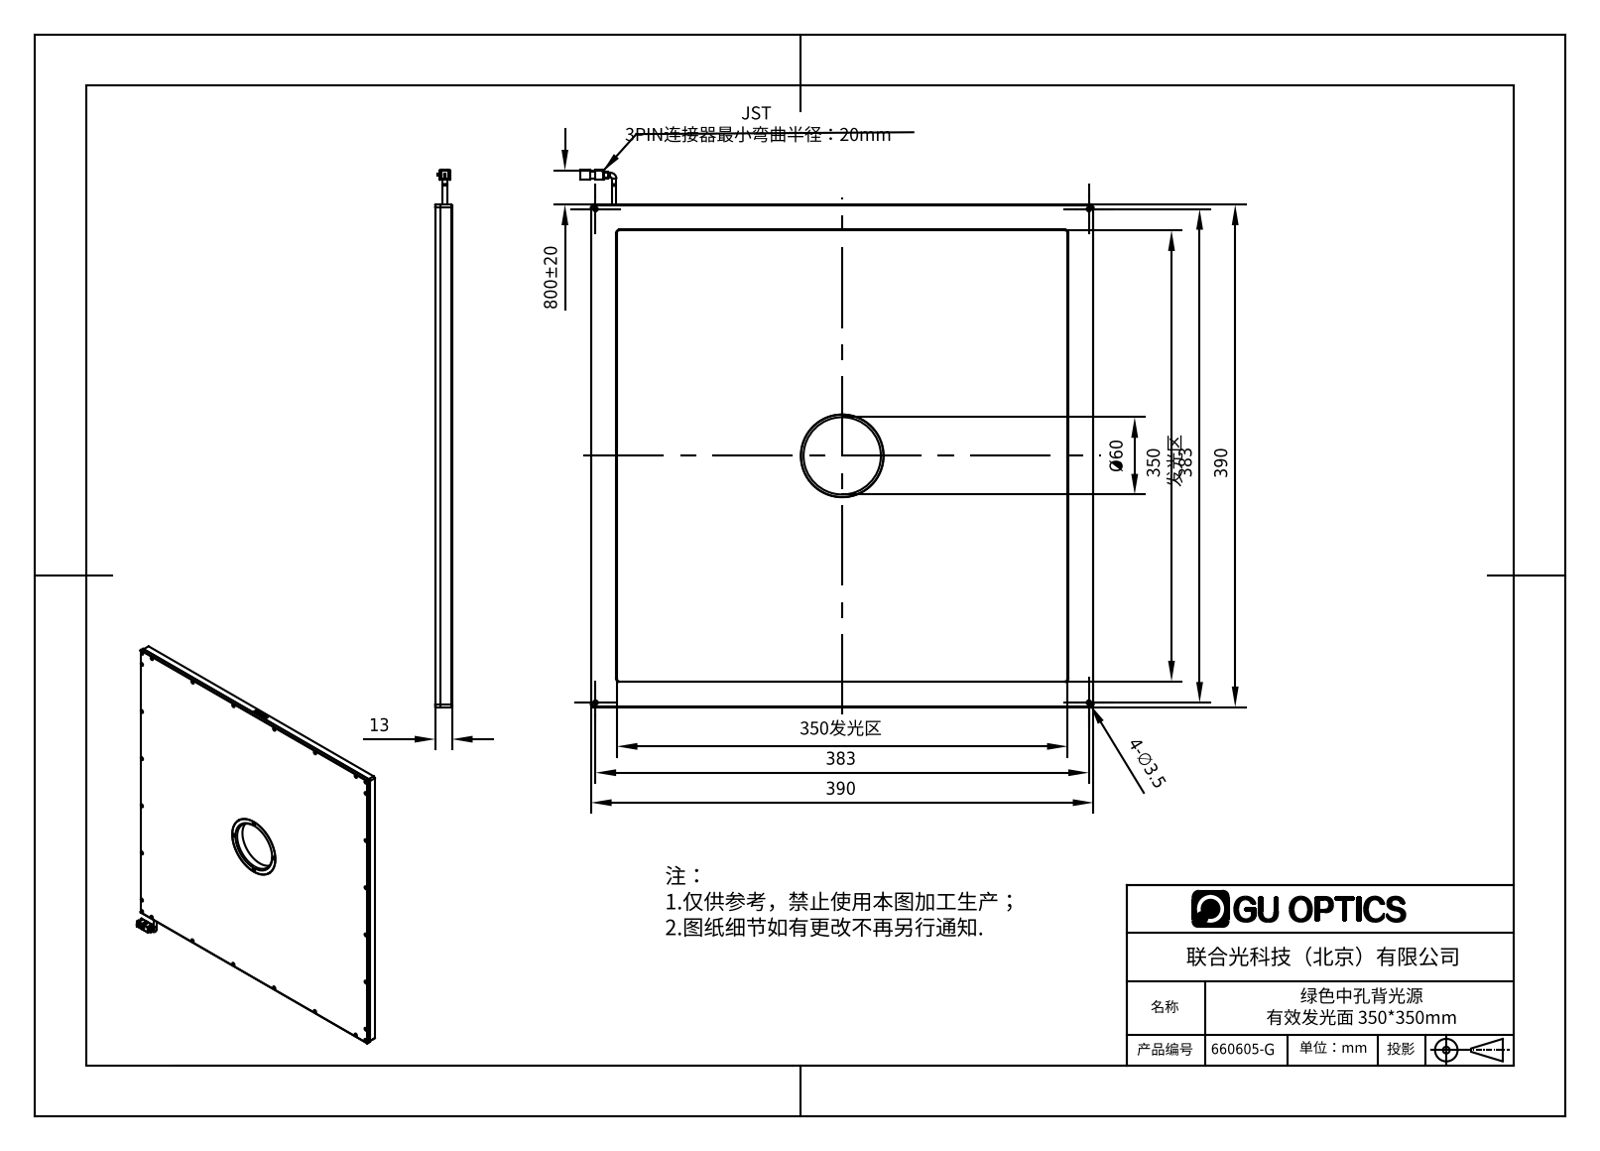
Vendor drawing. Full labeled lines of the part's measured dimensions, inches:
Part name (STEP PRODUCT): 660605-G
STEP written by: SolidWorks 2016 (AUTOMOTIVE_DESIGN)
Units: inches
Bodies: 6 solids, 510 faces (177 planar, 170 cylindrical, 163 other)
Overall size (bounding box): 16.417 × 15.689 × 0.512
Volume: 92.45 in³ · Surface area: 1 045 in²
Round holes (diameter × count): ⌀0.094 ×28, ⌀0.063 ×24, ⌀0.138 ×4, ⌀2.362 ×1, ⌀2.528 ×1, ⌀2.913 ×1
Round bosses / shafts (diameter × count): ⌀0.138 ×2, ⌀2.906 ×1, ⌀2.52 ×1
Partial cylindrical surfaces — rounded edges, fillets, slot ends (radius × count): R0.02 ×8, R0.079 ×8, R0.039 ×4, R0.118 ×4, R0.059 ×2
Main face-to-face distances: 0.157, 0.236, 0.394, 0.354, 0.118, 0.512, 0.02, 0.256, 0.098, 0.413
Hole centre spacings: 2.756, 15.367, 5.512, 16.091, 8.268, 15.118, 17.231, 0.65
